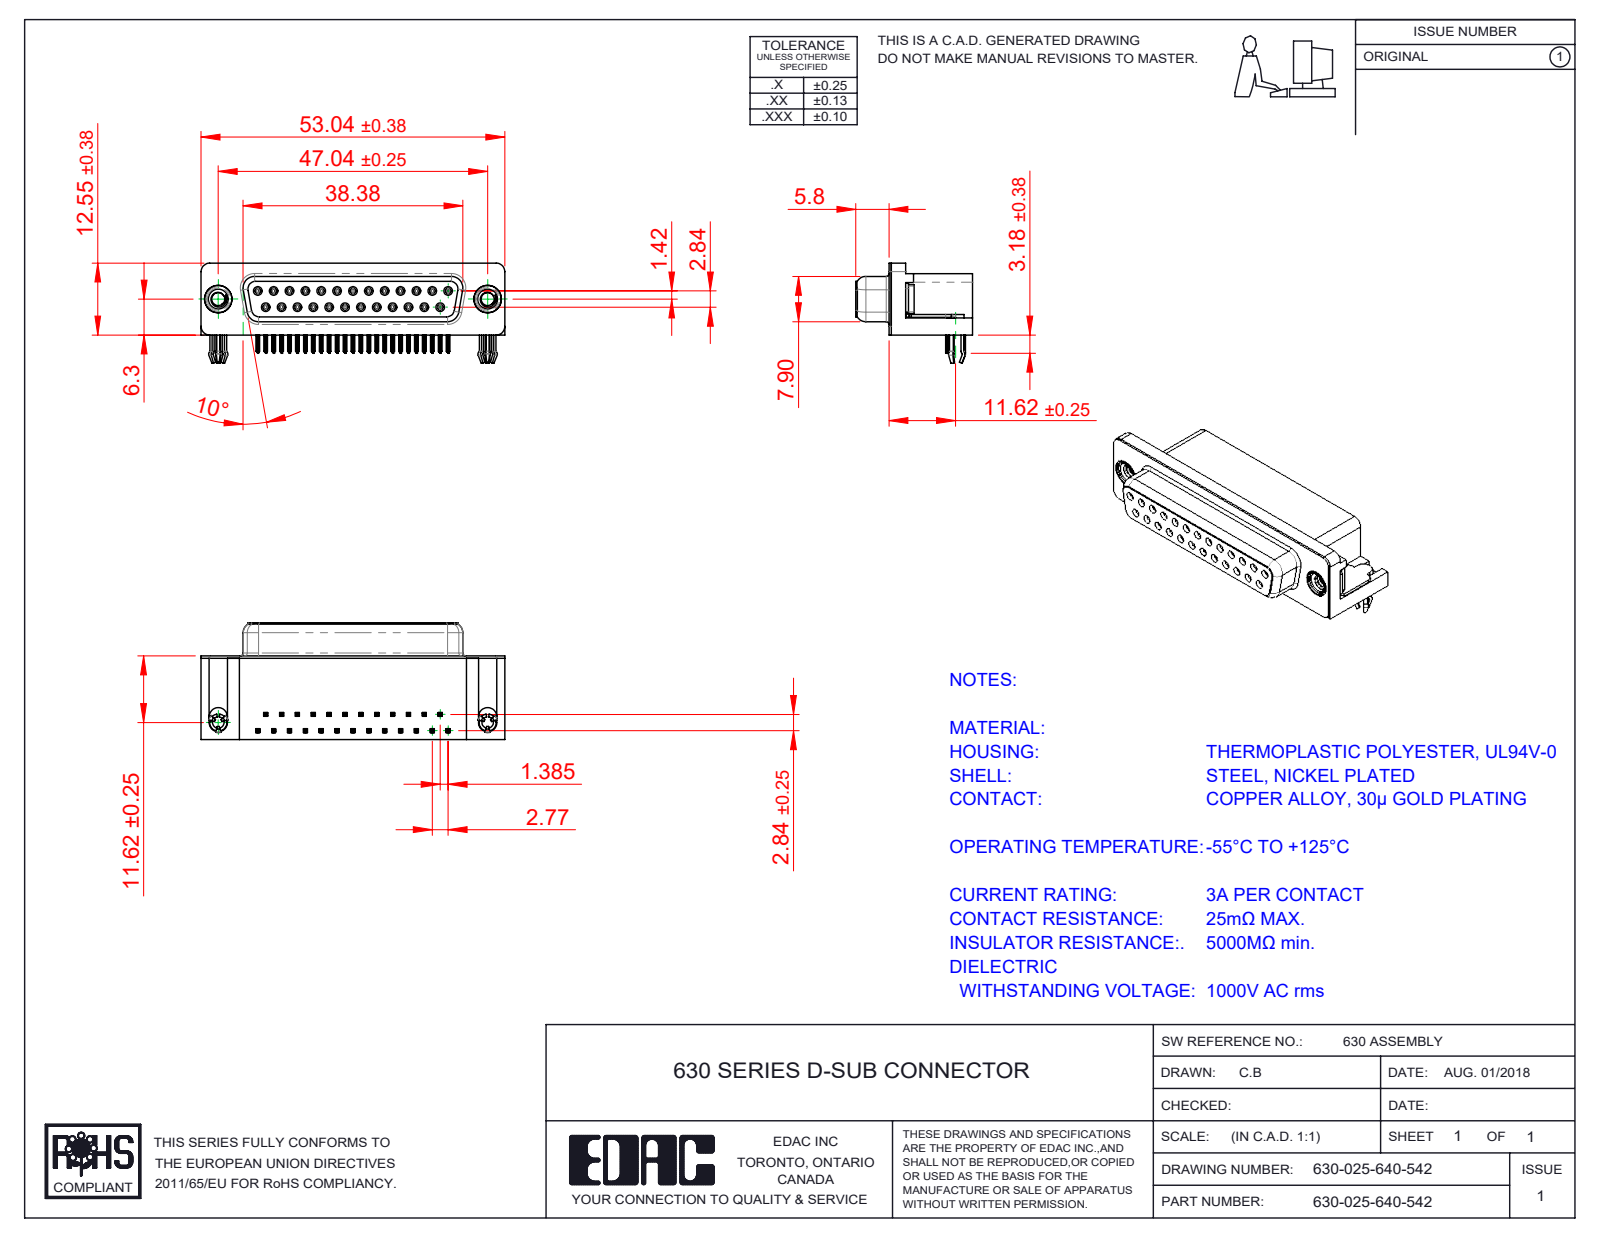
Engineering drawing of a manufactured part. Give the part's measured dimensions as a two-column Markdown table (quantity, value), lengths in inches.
| quantity | value |
| --- | --- |
| part name | 630 3 Prong Board Lock; 630-025-640-542; 630 4-40 Threaded Rivet; 630 Housing_25 Socket (+3 more) |
| STEP written by | SolidWorks 2020 (CONFIG_CONTROL_DESIGN) |
| units | inches |
| bodies | 31 solids, 3954 faces (1760 planar, 926 cylindrical, 1268 other) |
| overall size | 2.088 × 0.803 × 0.688 |
| volume | 0.525 in³ |
| surface area | 15.76 in² |
| round holes (diameter × count) | 0.031 × 25, 0.035 × 25, 0.079 × 2, 0.089 × 2, 0.157 × 2, 0.189 × 2, 0.197 × 2 |
| round bosses / shafts (diameter × count) | 0.047 × 25, 0.193 × 2, 0.187 × 2, 0.154 × 2, 0.118 × 2 |
| partial cylindrical surfaces (radius × count) | 0.004 × 200, 0.006 × 100, 0.014 × 50, 0.013 × 25, 0.039 × 18, 0.01 × 12, 0.011 × 12, 0.053 × 8 |
| main face-to-face distances | 0.016, 0.244, 0.407, 0.559, 0.107, 0.033, 0.262, 0.575, 0.112, 0.114 |
| hole center spacings | 0.124, 0.109, 0.218, 0.327, 0.436, 0.198, 0.198, 0.294 |
